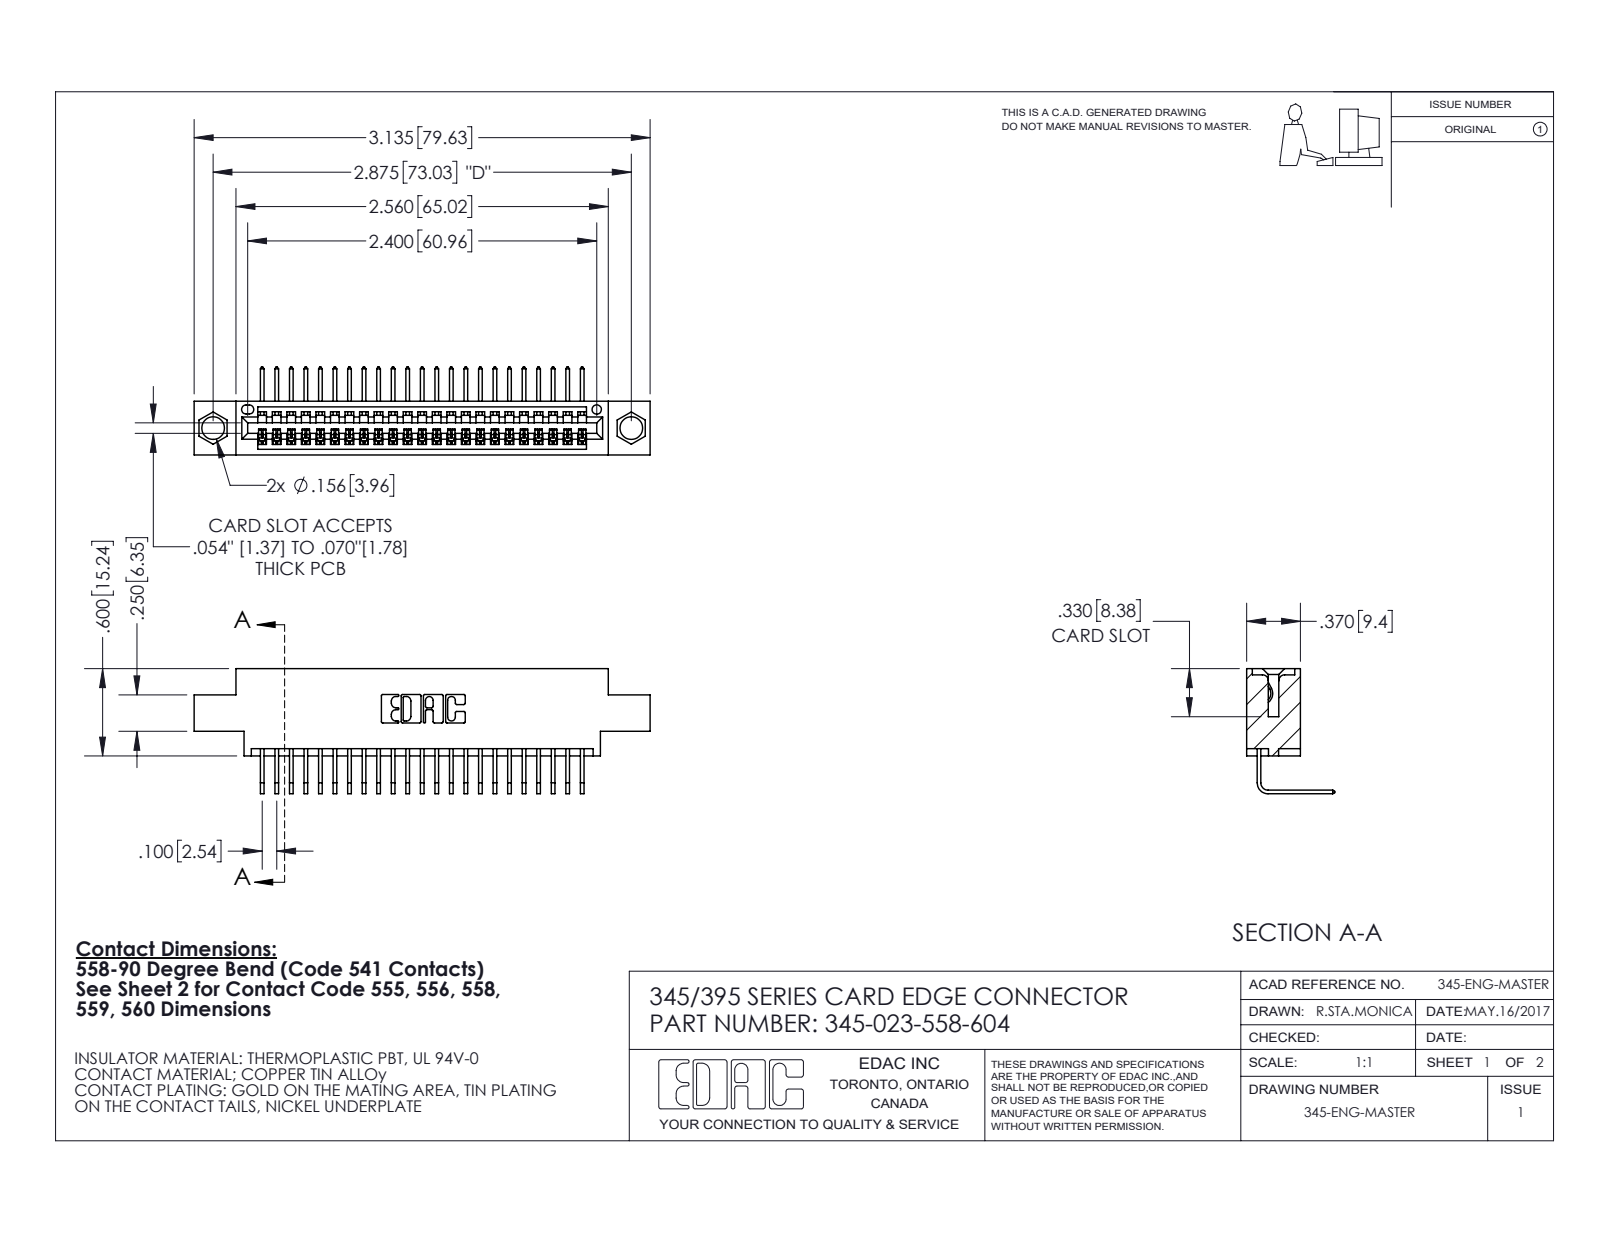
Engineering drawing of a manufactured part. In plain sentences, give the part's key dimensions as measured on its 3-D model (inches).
The part is named "345 Part_0.170 Offset - 0.156 Dia-TI; 345-292-001_558 Tail - 2; 345-023-558-604". Its 3-D file was written by "SolidWorks 2020 (CONFIG_CONTROL_DESIGN)". It is 24 solids with 1524 faces: 1064 planar, 460 cylindrical and 0 other. Overall it measures 3.135 by 0.859 by 0.605 inches. Its volume is 0.443 cubic inches and its surface area 15.21 square inches. Round holes: 2 of diameter 0.156, 1 of diameter 0.064. Partial cylindrical surfaces (rounded edges, fillets, slot ends): 46 of radius 0.006, 22 of radius 0.01, 6 of radius 0.007, 6 of radius 0.031, 3 of radius 0.026, 2 of radius 0.031, 2 of radius 0.04, 1 of radius 0.014. The main face-to-face distances are 0.072, 0.298, 0.37, 0.2, 0.098, 0.272, 0.025, 0.225, 0.175, 0.149. The hole center spacings are 0.27, 2.641, 2.875.
